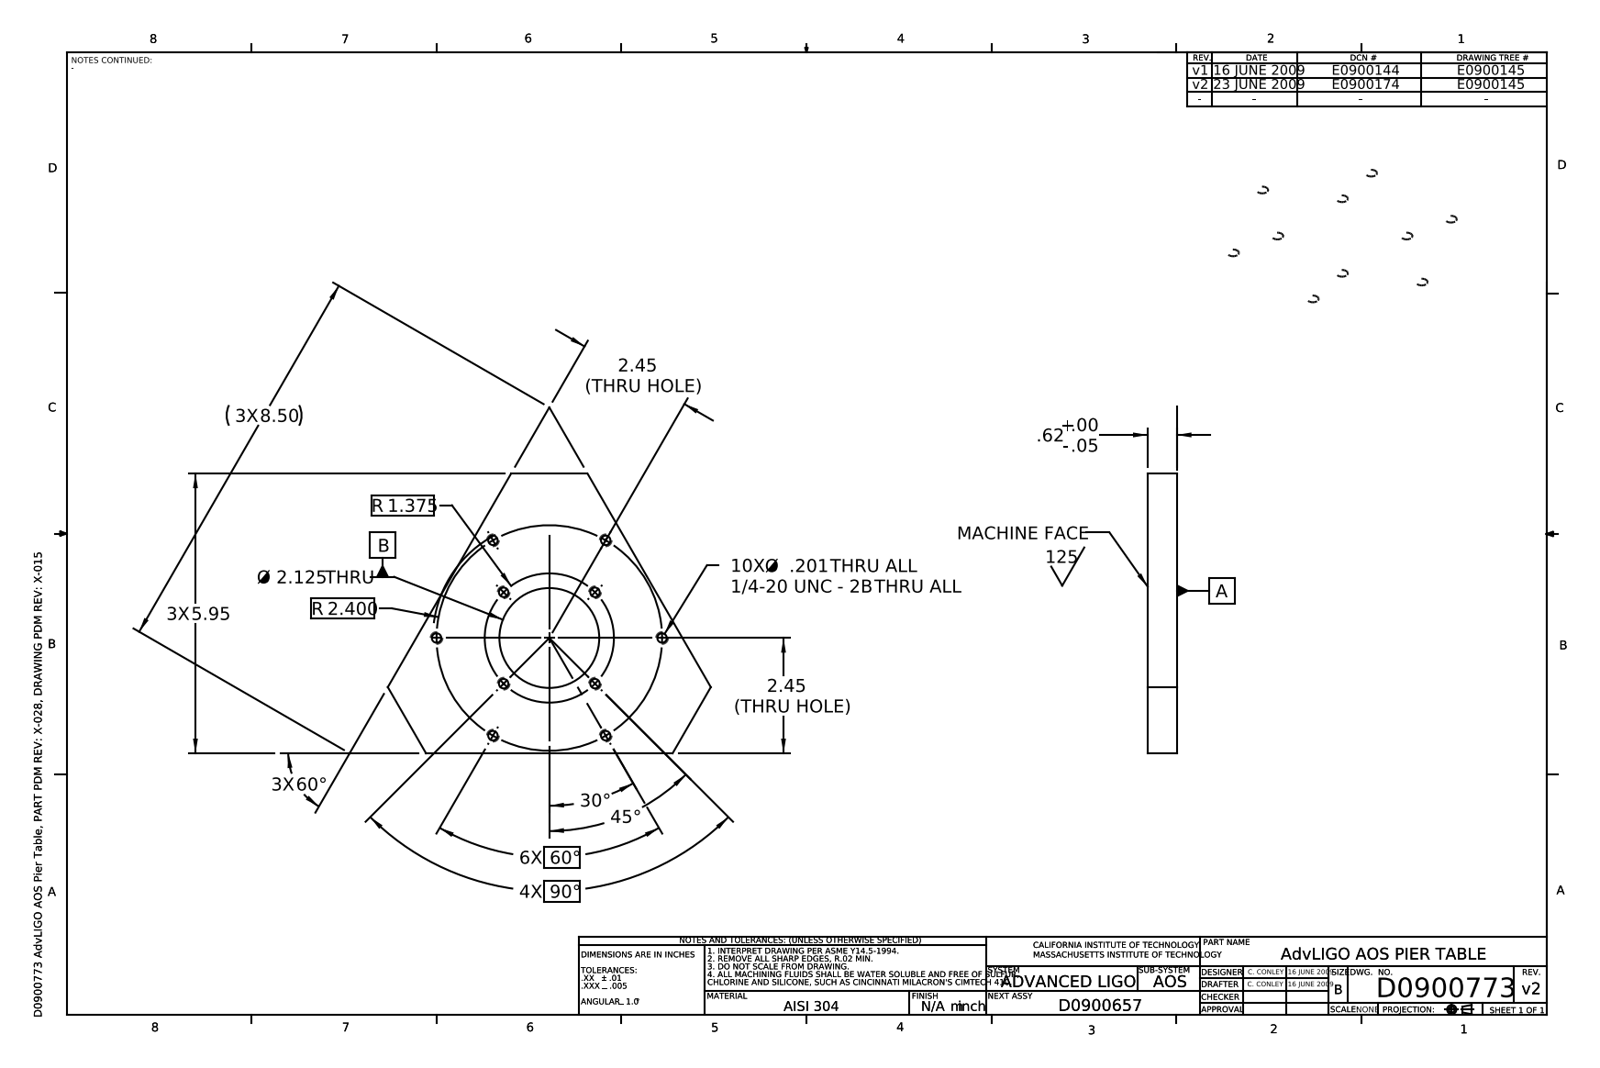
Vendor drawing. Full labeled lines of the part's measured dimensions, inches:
Part name (STEP PRODUCT): D0900773 AdvLIGO AOS Pier Table
STEP written by: SolidWorks 2009 (AUTOMOTIVE_DESIGN)
Units: inches
Bodies: 1 solid, 30 faces (8 planar, 22 cylindrical, 0 other)
Overall size (bounding box): 6.875 × 5.954 × 0.375
Volume: 8.996 in³ · Surface area: 60.59 in²
Round holes (diameter × count): ⌀0.201 ×10, ⌀2.125 ×1
Main face-to-face distances: 0.375, 5.954
Hole centre spacings: 2.4, 4.157, 1.129, 1.375, 1.727, 1.945, 2.438, 3.059
